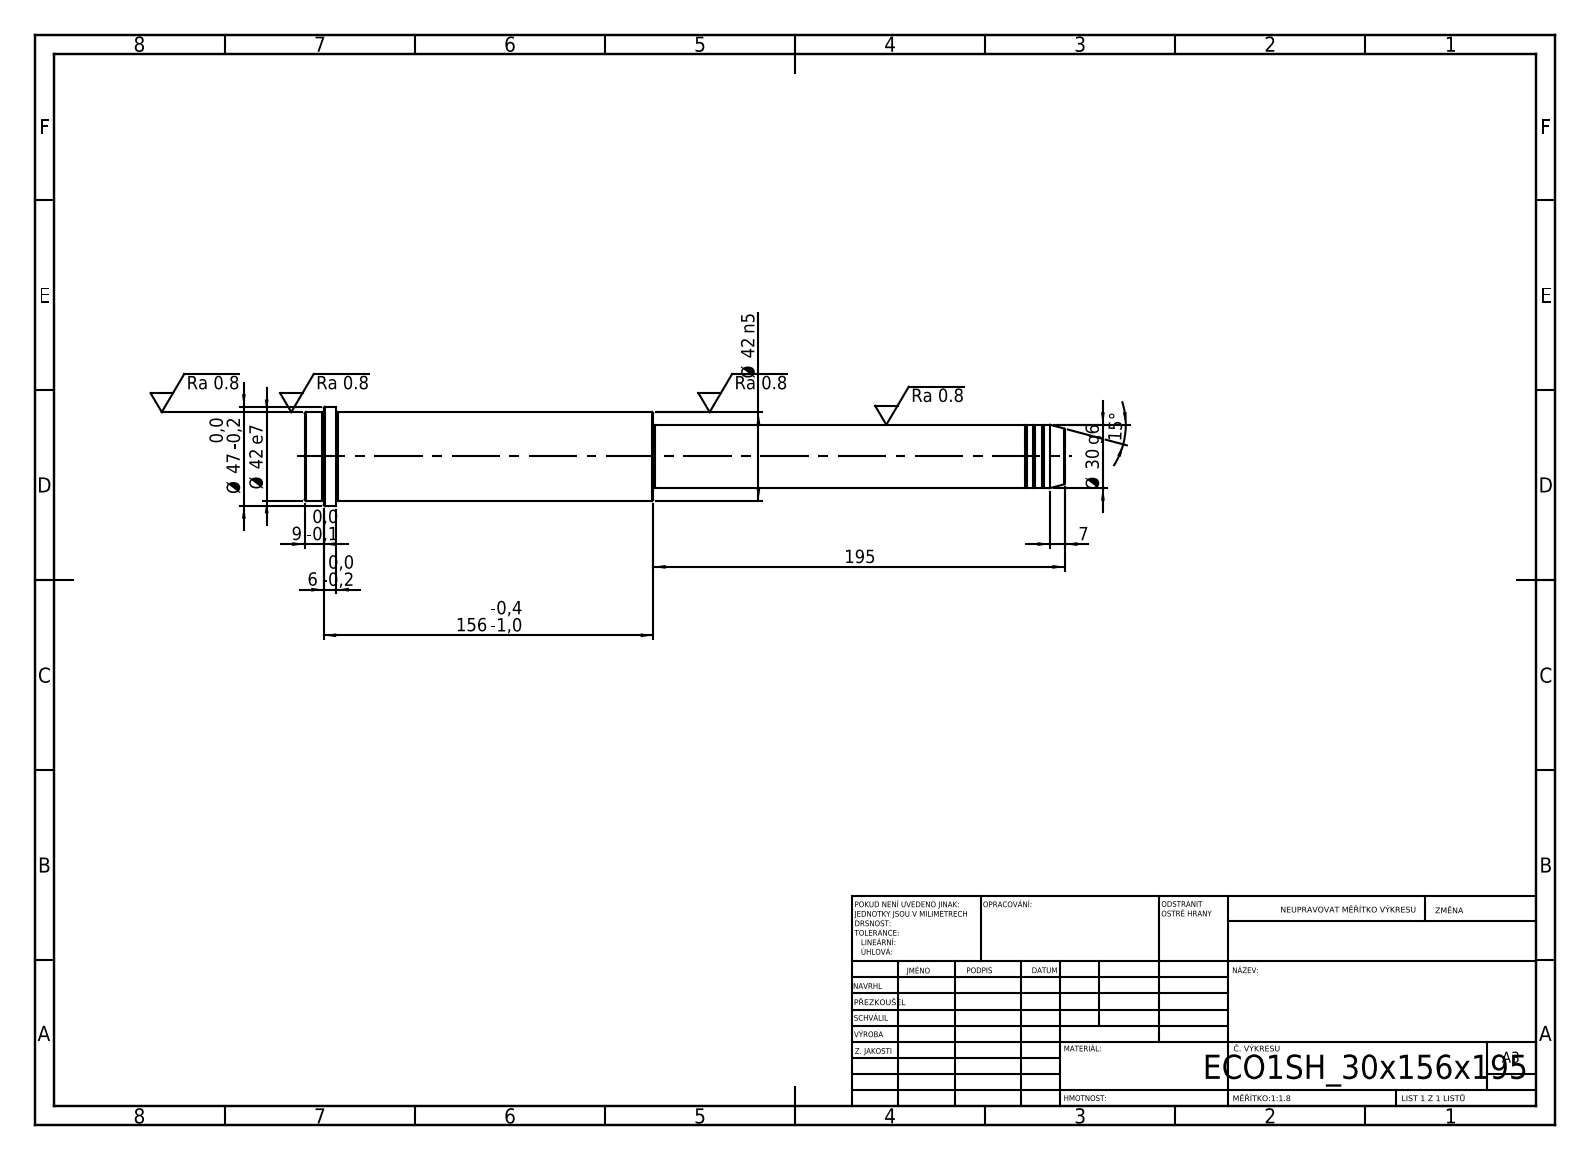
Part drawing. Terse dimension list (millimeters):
written by: SolidWorks 2019 (CONFIG_CONTROL_DESIGN)
unit: mm
bodies: 1 solid, 52 faces (6 planar, 16 cylindrical, 30 other)
size: 360 × 47 × 47
volume: 367 628 mm³; area: 43 783 mm²
bosses: 1× ⌀47, 1× ⌀42, 1× ⌀30, 1× ⌀29
face distances: 165, 195, 360, 345, 150, 15, 351, 156, 6, 9
